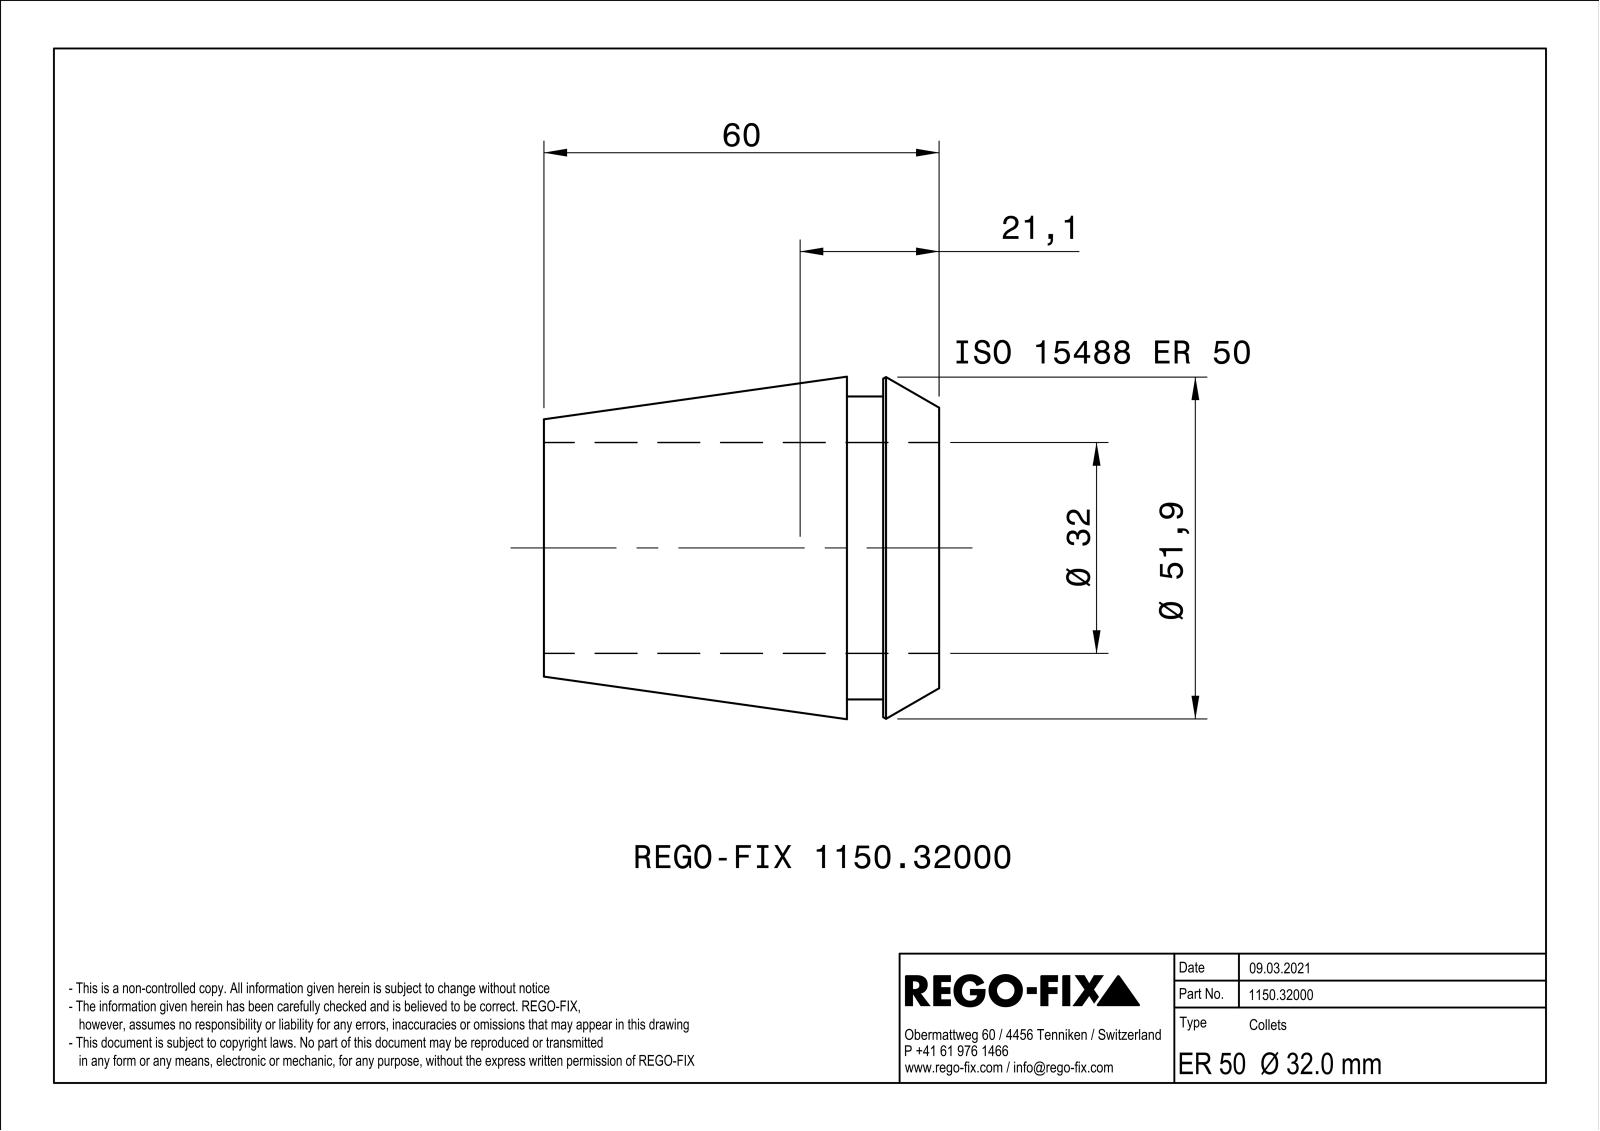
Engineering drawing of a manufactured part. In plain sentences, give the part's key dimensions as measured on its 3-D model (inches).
The part is named "NOCUT". Its 3-D file was written by "SIEMENS PLM Software Solid Edge ST10 (AUTOMOTIVE_DESIGN)". It is 1 solid with 177 faces: 88 planar, 9 cylindrical and 80 other. Overall it measures 2.362 by 2.047 by 2.047 inches. Its volume is 2.772 cubic inches and its surface area 41.71 square inches. Round holes: 1 of diameter 1.26. Round bosses or shafts: 1 of diameter 1.811. The main face-to-face distances are 0.039, 0.551, 0.335, 0.217, 2.362, 2.028, 1.811, 0.354, 0.02, 0.197.
